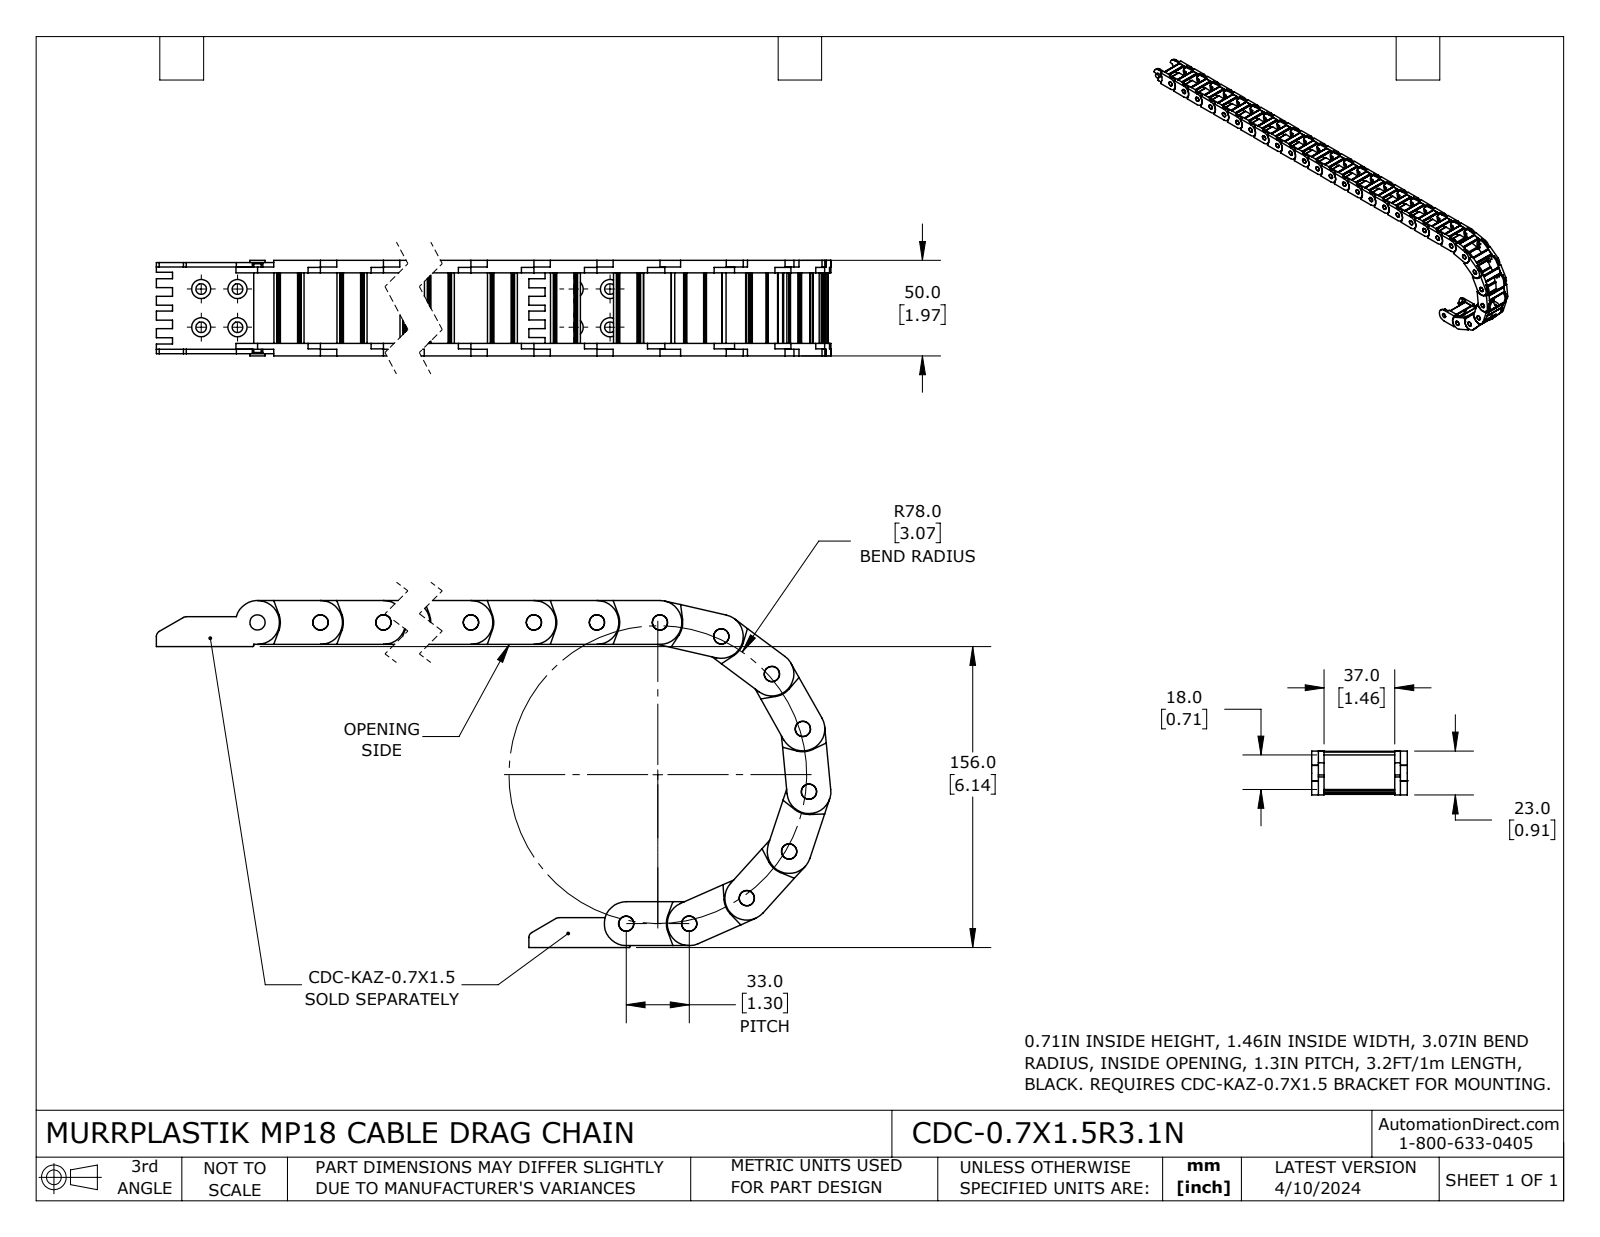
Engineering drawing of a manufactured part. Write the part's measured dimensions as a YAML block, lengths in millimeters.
part_name: "CDC-0.7X1.5R3.1N"
step_written_by: "SolidWorks 2023 (CONFIG_CONTROL_DESIGN)"
units: millimeters
bodies: {solids: 30, faces: 2370, planar: 1110, cylindrical: 1260, other: 0}
overall_size: [826.89, 180.72, 50]
volume: 323575
surface_area: 243788
round_holes:
  - {diameter: 8, count: 30}
round_bosses_or_shafts:
  - {diameter: 8, count: 1}
partial_cylinders:
  - {radius: 0.5, count: 120}
  - {radius: 1.5, count: 120}
  - {radius: 0.2, count: 60}
  - {radius: 0.3, count: 60}
  - {radius: 11.5, count: 31}
  - {radius: 11.95, count: 31}
  - {radius: 5, count: 30}
  - {radius: 5.45, count: 30}
face_to_face_distances: [6.5, 43.5, 50, 3.5, 46.5, 3, 40, 3.7, 46.3, 42.8]
hole_center_spacings: [33, 66, 99, 132, 165, 198, 231, 264]
